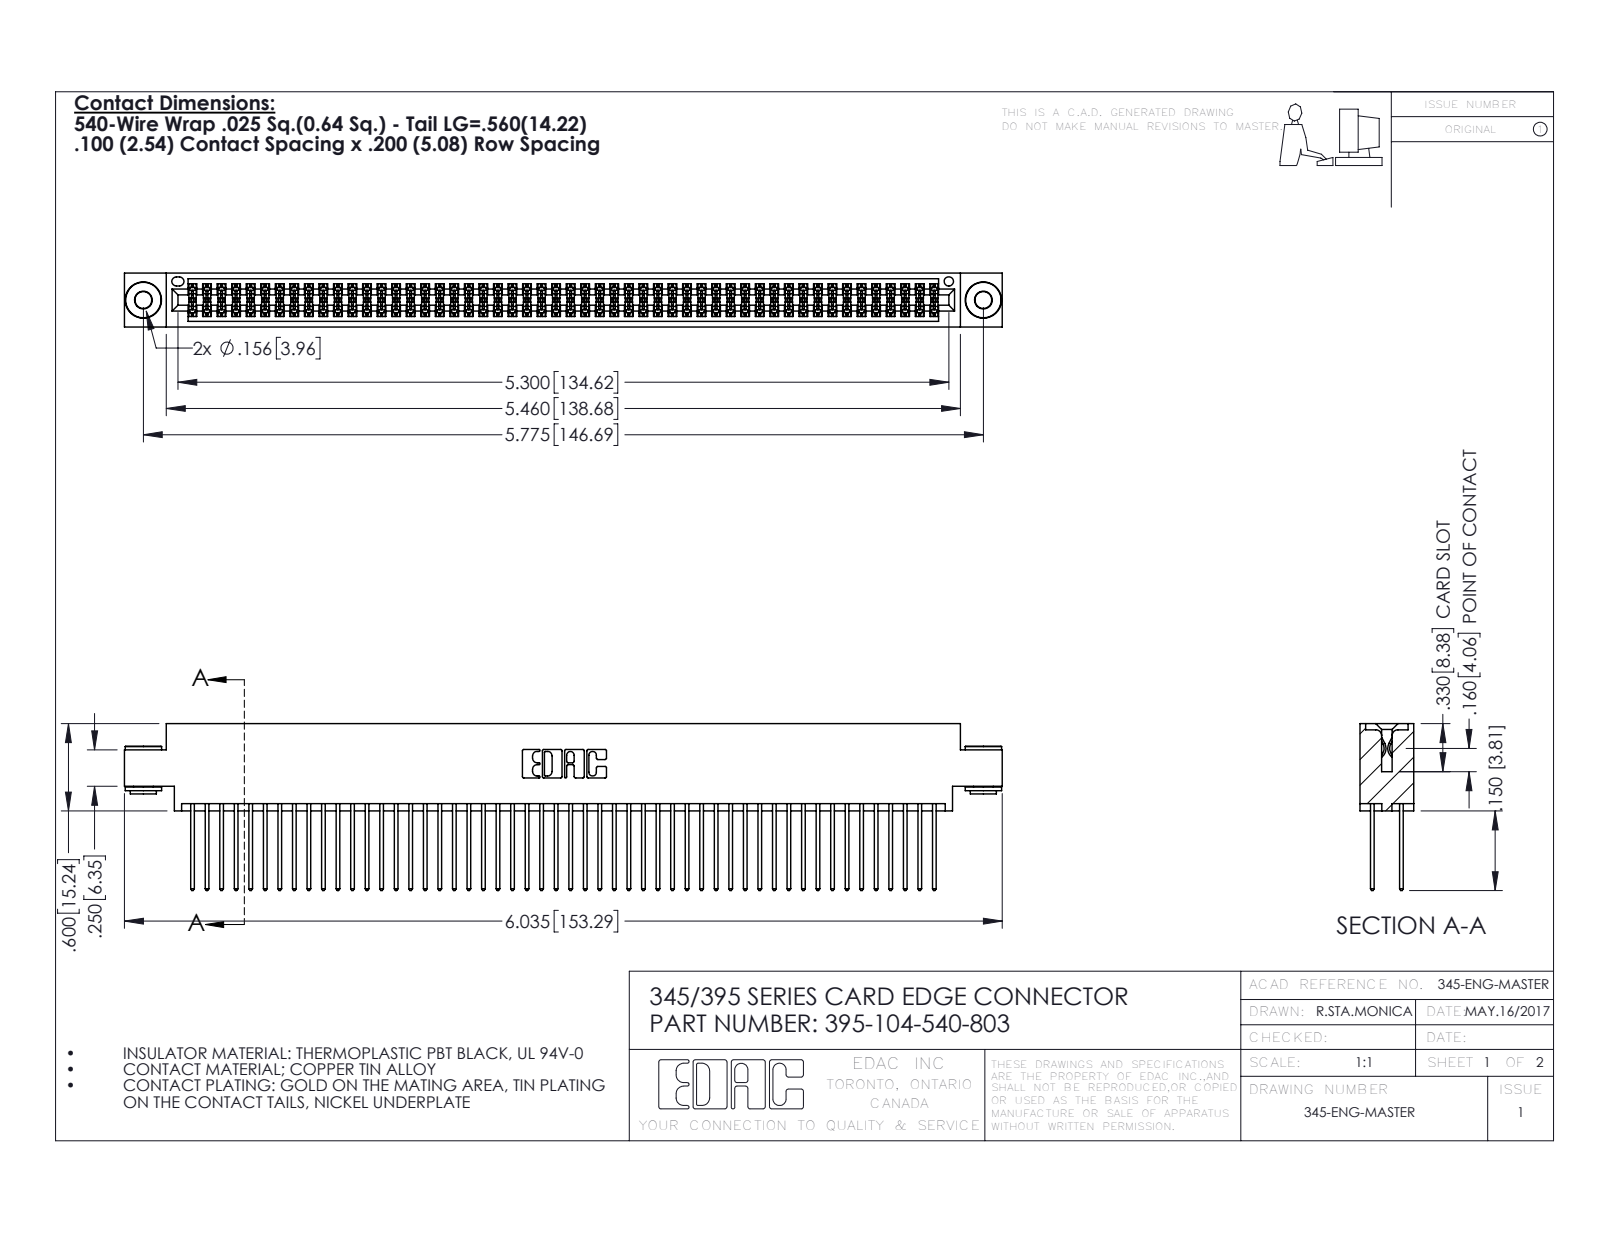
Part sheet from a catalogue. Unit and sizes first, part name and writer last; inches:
Units: inches
Overall size (bounding box): 6.035 × 1.147 × 0.37
Round holes (diameter × count): ⌀0.116 ×2, ⌀0.156 ×2, ⌀0.064 ×1
Round bosses / shafts (diameter × count): ⌀0.25 ×2, ⌀0.18 ×2, ⌀0.136 ×2
Partial cylindrical surfaces — rounded edges, fillets, slot ends (radius × count): R0.006 ×156, R0.01 ×104, R0.01 ×22, R0.007 ×6, R0.031 ×6, R0.026 ×3, R0.014 ×2, R0.019 ×2
Main face-to-face distances: 0.072, 0.298, 0.2, 0.098, 0.272, 0.025, 0.37, 0.225, 0.175, 0.149
Hole centre spacings: 0.27, 5.539, 5.775
Volume: 0.933 in³ · Surface area: 38.69 in²
Bodies: 107 solids, 5368 faces (3526 planar, 1834 cylindrical, 8 other)
Part name (STEP PRODUCT): 395-104-540-803; 345-250-002_345-250-002-102; 345-292-001_345-293-140; 345 Part_0.170 Offset - 0.156 Dia-TH
STEP written by: SolidWorks 2016 (CONFIG_CONTROL_DESIGN)
